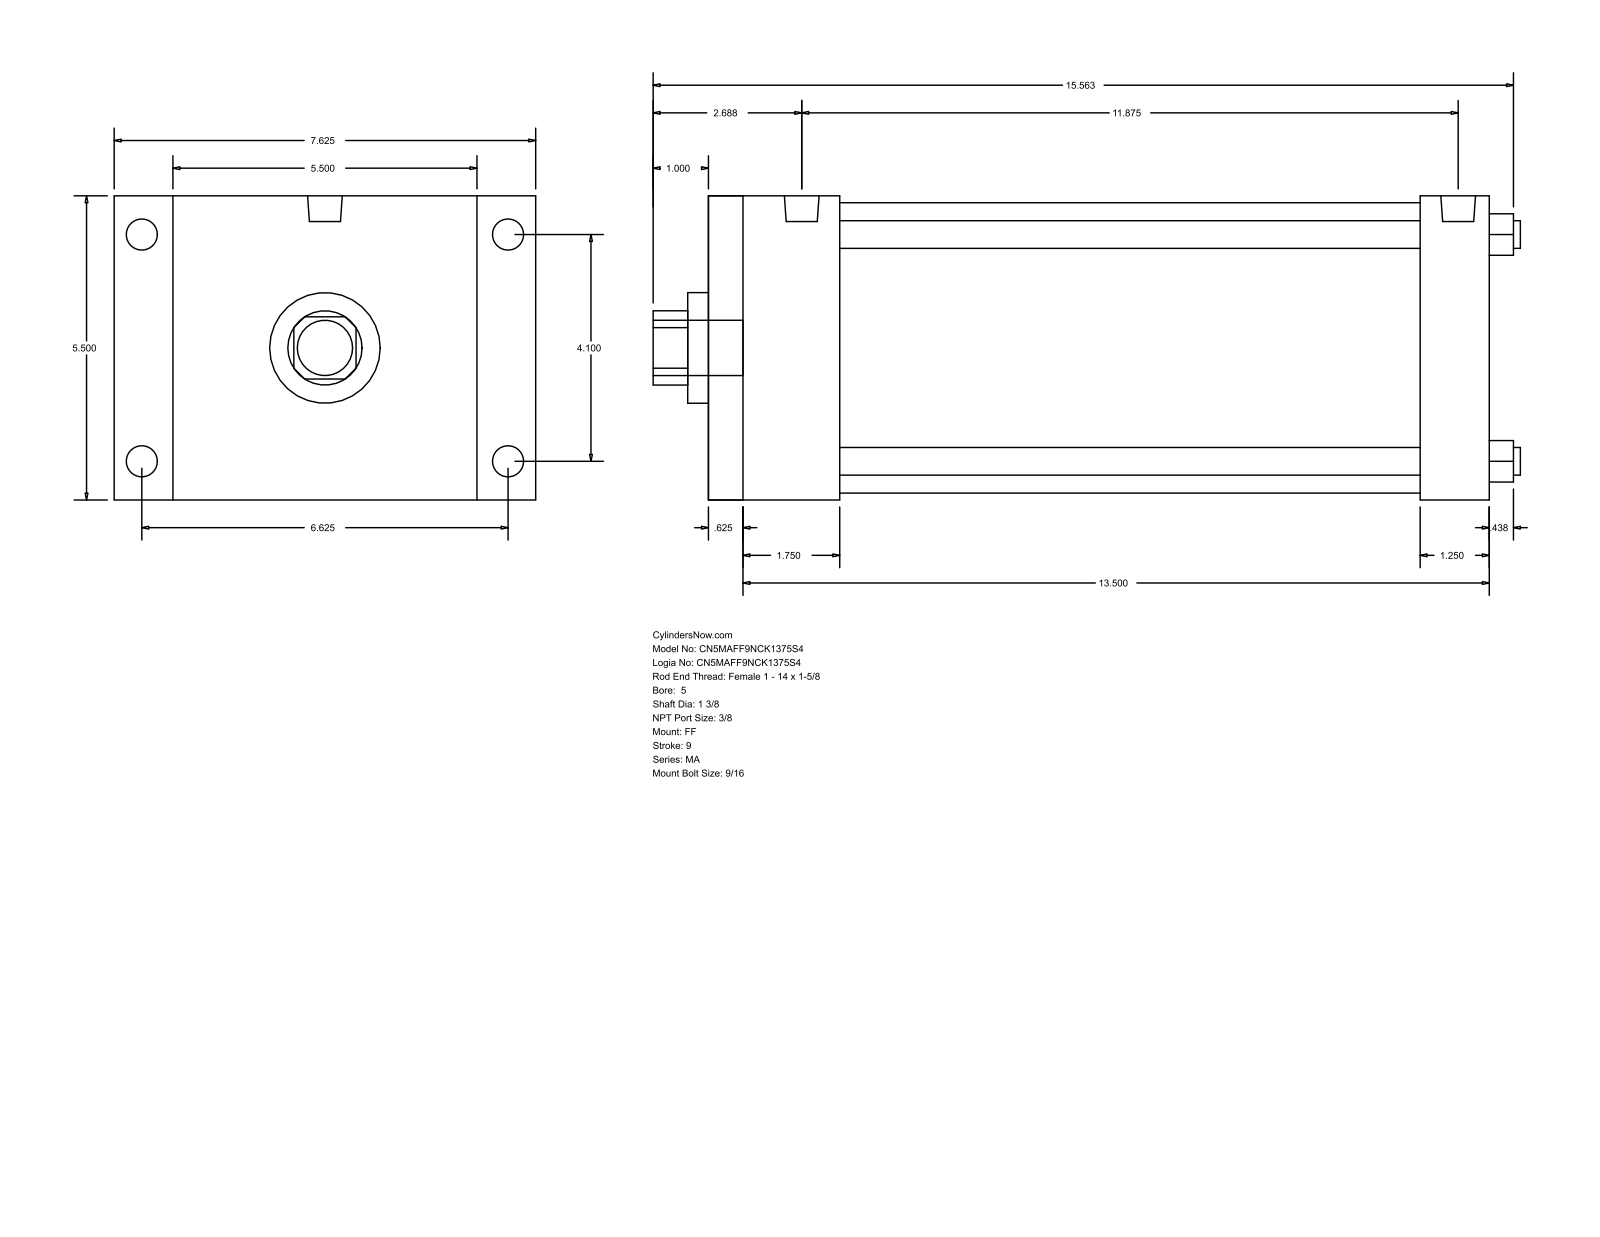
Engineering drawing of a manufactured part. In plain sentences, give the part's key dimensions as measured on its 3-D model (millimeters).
The part is named "MA_FF__0500_1.375". Its 3-D file was written by "GSSL Pune (CONFIG_CONTROL_DESIGN)". It is 0 solids with 92 faces: 64 planar, 28 cylindrical and 0 other. Overall it measures 398.46 by 193.68 by 139.7 millimeters. Round holes: 4 of diameter 12.7, 1 of diameter 34.92, 1 of diameter 50.8, 1 of diameter 133.35. Round bosses or shafts: 4 of diameter 14.29, 4 of diameter 11.11, 2 of diameter 15.93, 1 of diameter 25.4. Partial cylindrical surfaces (rounded edges, fillets, slot ends): 1 of radius 17.06. The main face-to-face distances are 139.7, 358.78, 15.87, 342.91, 327.03, 311.16, 31.75, 60.32, 44.45, 266.71. The hole center spacings are 73.64, 104.14, 147.28.
